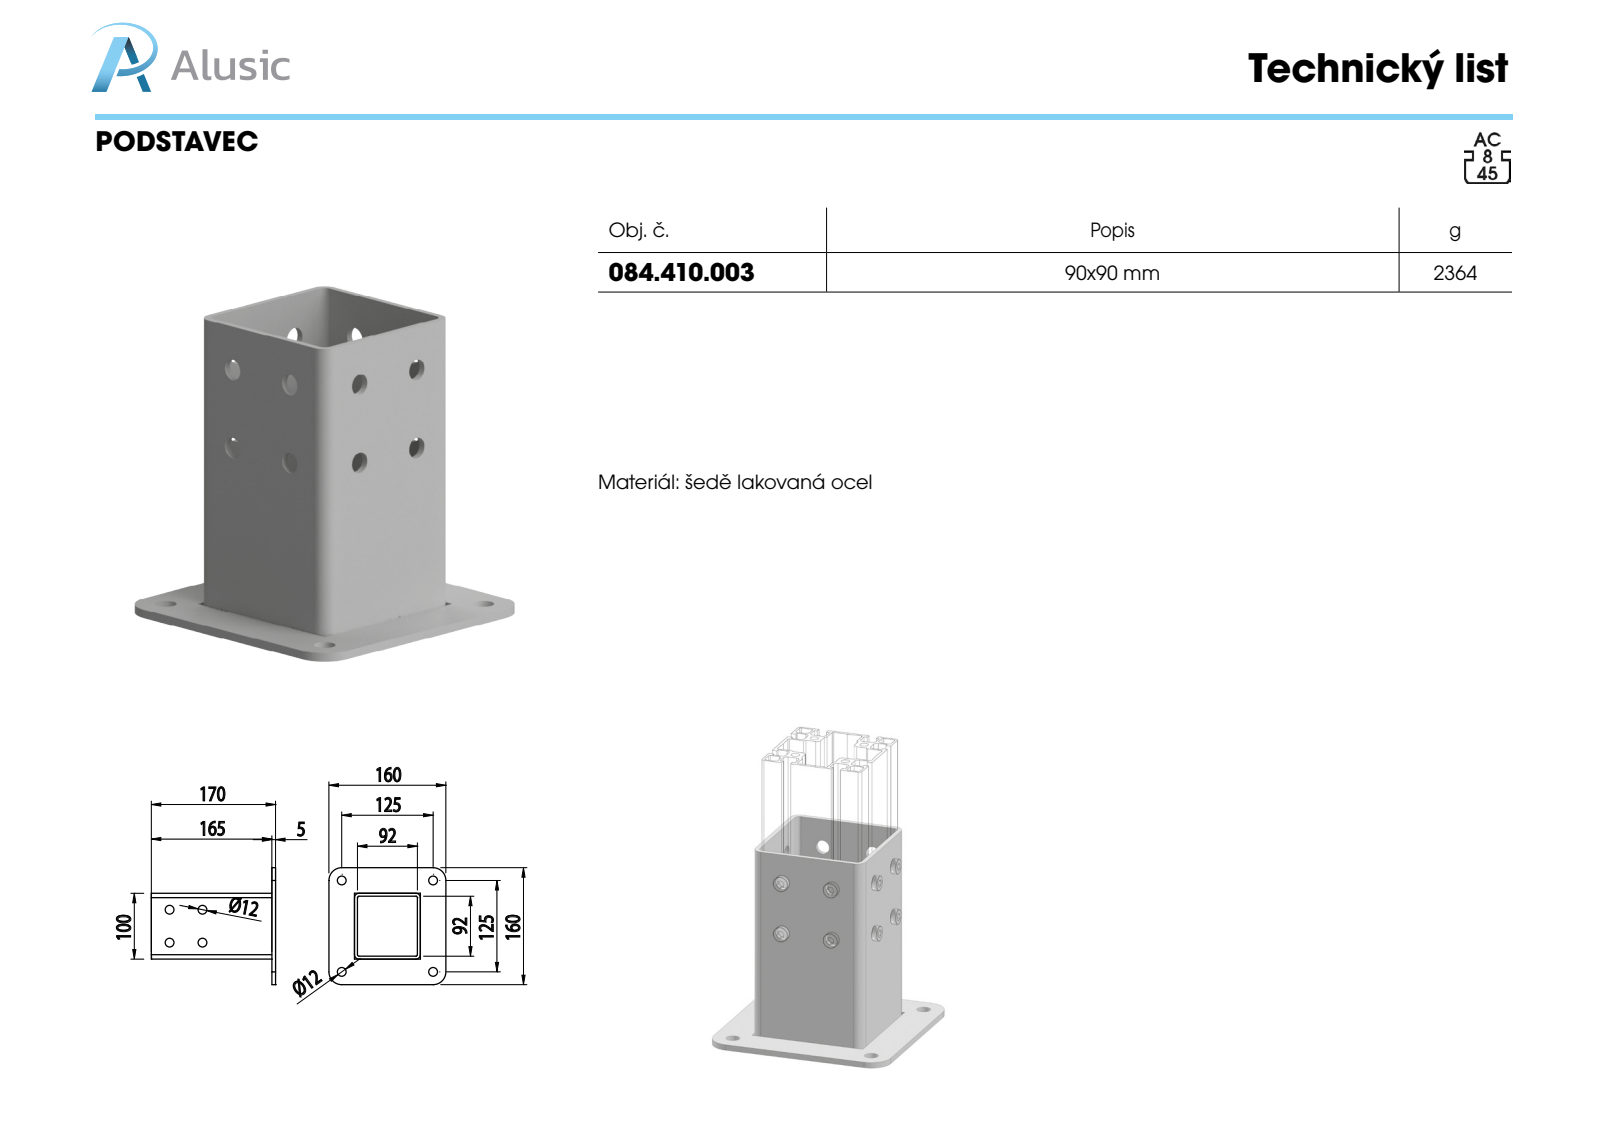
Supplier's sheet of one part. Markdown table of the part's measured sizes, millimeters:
| quantity | value |
| --- | --- |
| part name | 084.410.003 |
| STEP written by | SolidWorks 2011 (CONFIG_CONTROL_DESIGN) |
| units | millimeters |
| bodies | 2 solids, 72 faces (20 planar, 52 cylindrical, 0 other) |
| overall size | 170 × 160 × 160 |
| volume | 321 101 mm³ |
| surface area | 164 338 mm² |
| round holes (diameter × count) | 12 × 12 |
| partial cylindrical surfaces (radius × count) | 4 × 4, 8 × 4, 17.5 × 4 |
| main face-to-face distances | 4, 96, 92, 100, 5, 30, 34, 126, 130, 29.9 |
| hole center spacings | 45, 63.64, 125, 176.78 |
